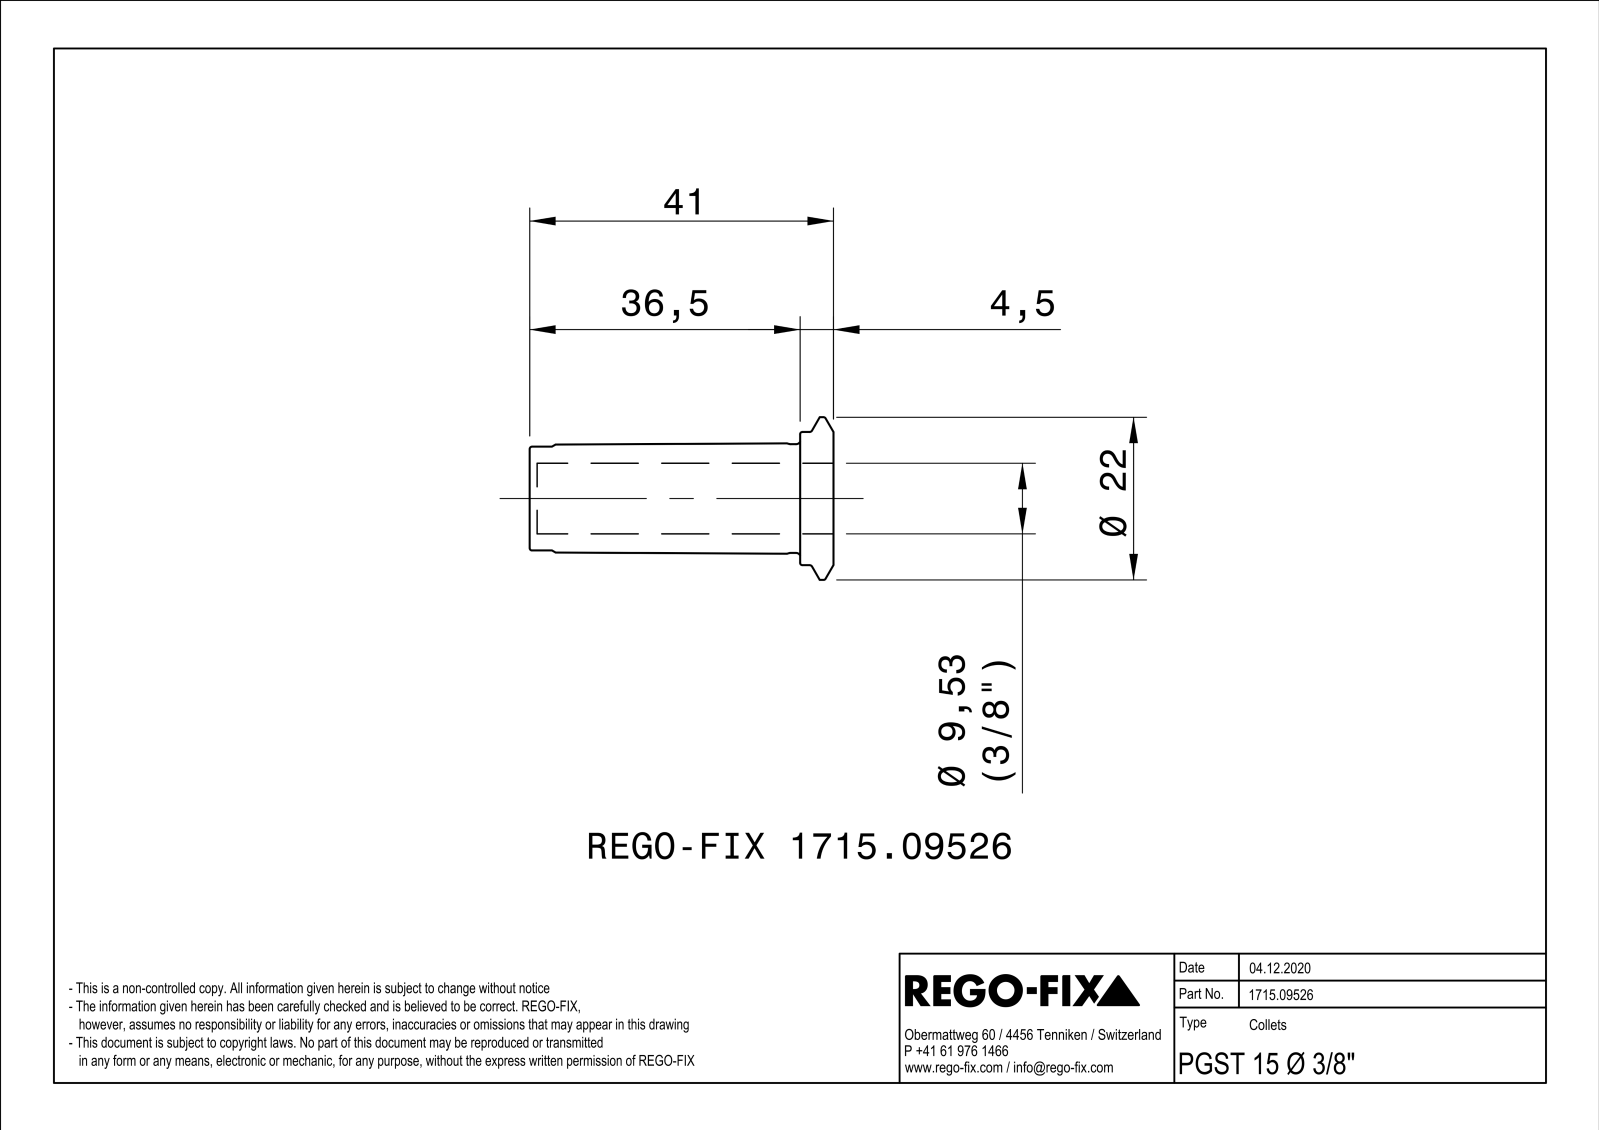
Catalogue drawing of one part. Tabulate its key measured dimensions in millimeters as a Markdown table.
| quantity | value |
| --- | --- |
| part name | NOCUT |
| STEP written by | SIEMENS PLM Software Solid Edge ST10 (AUTOMOTIVE_DESIGN) |
| units | millimeters |
| bodies | 2 solids, 48 faces (12 planar, 14 cylindrical, 22 other) |
| overall size | 41 × 21.98 × 21.98 |
| volume | 4 902 mm³ |
| surface area | 4 160 mm² |
| round holes (diameter × count) | 1.5 × 3, 3 × 1, 9.52 × 1, 10 × 1, 11.46 × 1, 12.5 × 1 |
| round bosses / shafts (diameter × count) | 21.98 × 1, 18 × 1, 14.7 × 1, 14 × 1, 12 × 1, 11.1 × 1 |
| main face-to-face distances | 4.5, 36.5, 41, 32, 36, 31.5, 0.5, 5, 2 |
| hole center spacings | 4, 6.93, 6.92 |
